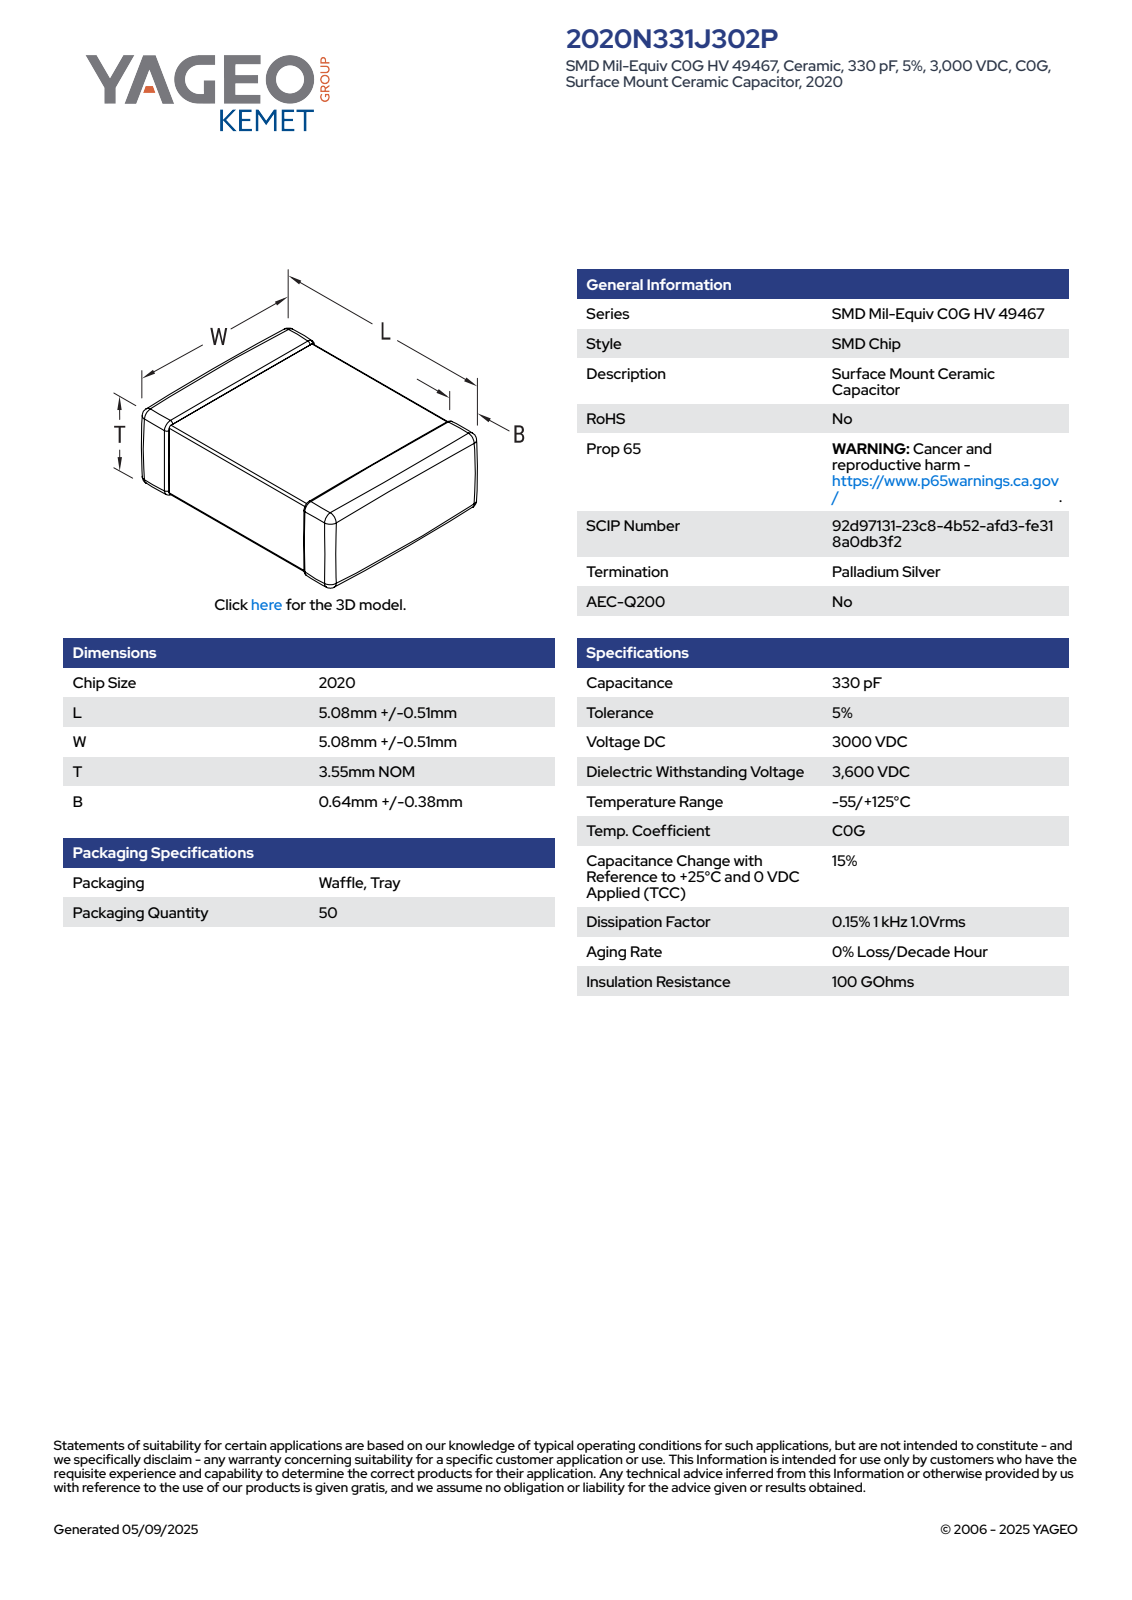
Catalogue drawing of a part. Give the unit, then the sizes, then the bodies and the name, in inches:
Units: inches
Overall size (bounding box): 0.22 × 0.22 × 0.14
Partial cylindrical surfaces — rounded edges, fillets, slot ends (radius × count): R0.005 ×24
Main face-to-face distances: 0.13, 0.22, 0.211, 0.135, 0.215, 0.14, 0.135, 0.131, 0.022, 0.104
Volume: 0.006 in³ · Surface area: 0.215 in²
Bodies: 4 solids, 125 faces (71 planar, 38 cylindrical, 16 other)
Part name (STEP PRODUCT): CCS_STDNOS_2020_L5.59W5.59T3.55B0.64
STEP written by: SolidWorks 2021 (AUTOMOTIVE_DESIGN)
